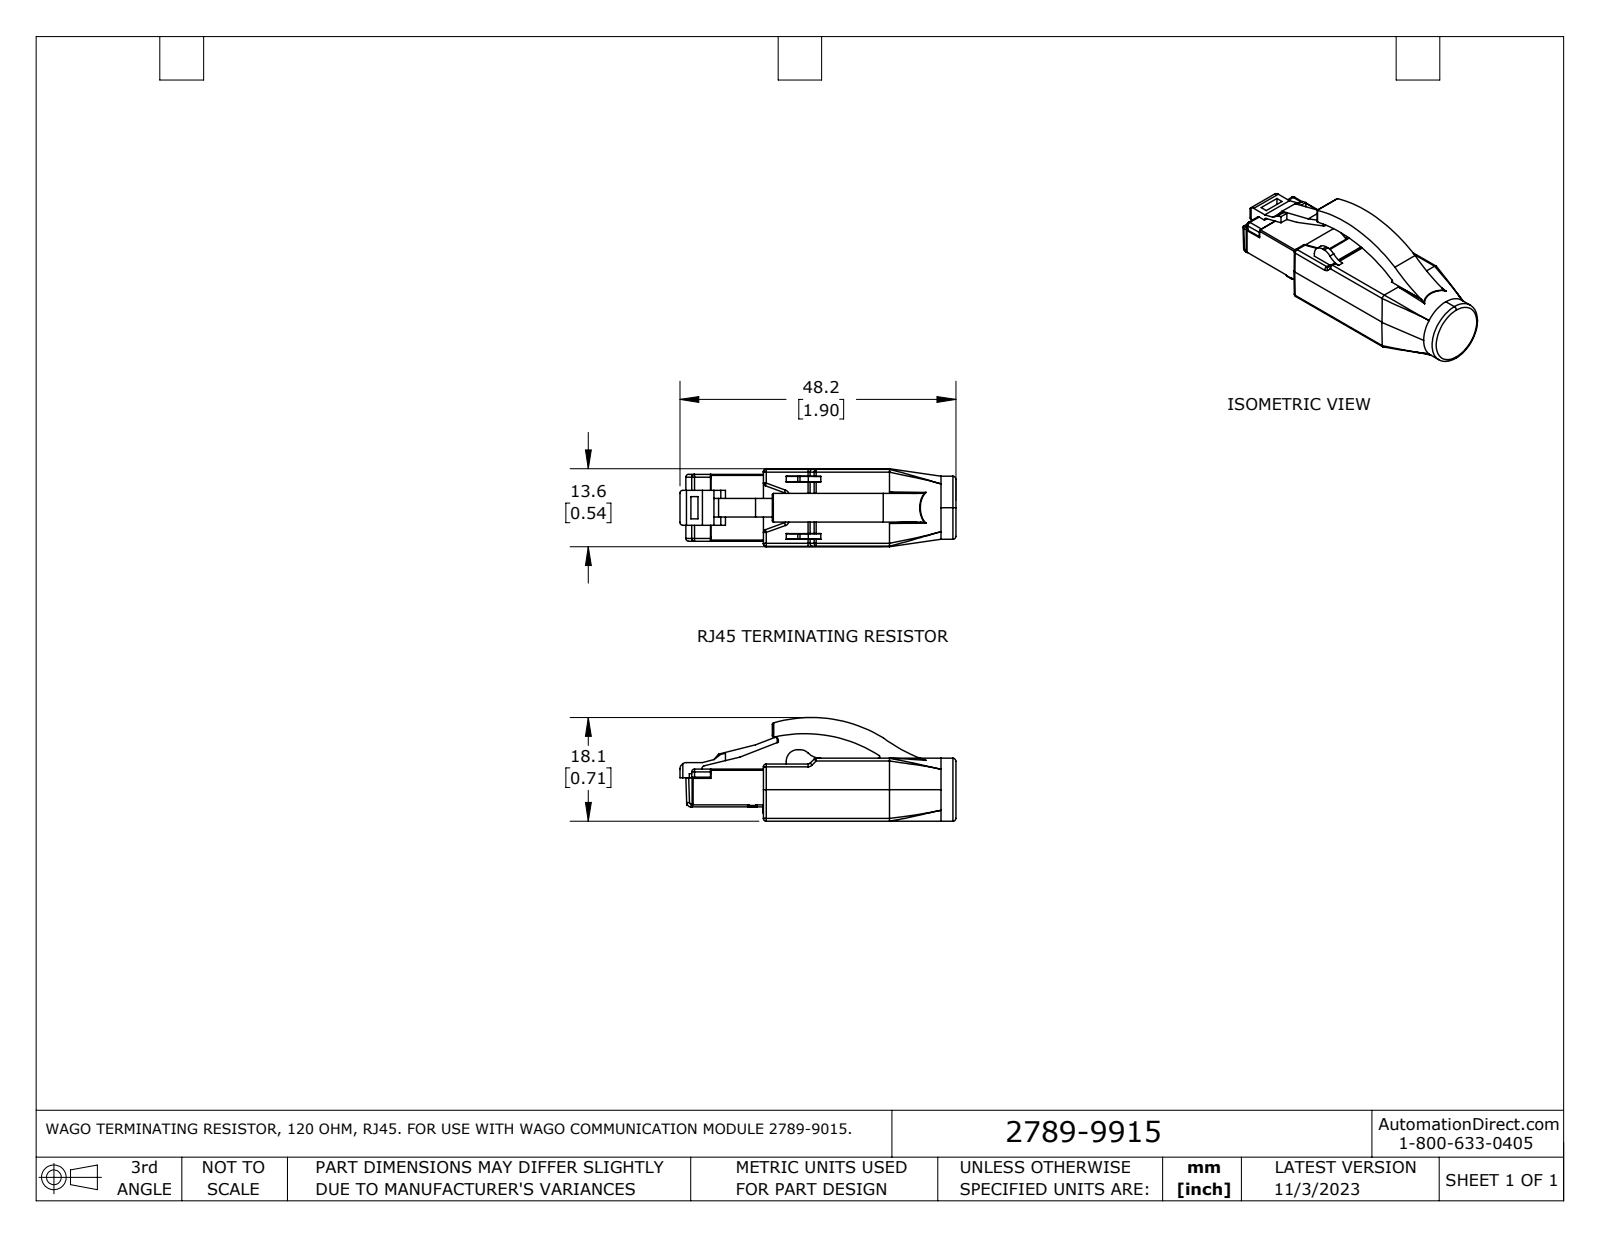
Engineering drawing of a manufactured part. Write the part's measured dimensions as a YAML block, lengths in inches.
part_name: "2789-9915"
step_written_by: "SolidWorks 2023 (AUTOMOTIVE_DESIGN)"
units: inches
bodies: {solids: 1, faces: 314, planar: 193, cylindrical: 90, other: 31}
overall_size: [1.897, 0.713, 0.536]
volume: 0.358
surface_area: 5.434
round_bosses_or_shafts:
  - {diameter: 0.433, count: 1}
partial_cylinders:
  - {radius: 0.02, count: 37}
  - {radius: 0.008, count: 15}
  - {radius: 0.01, count: 5}
  - {radius: 0.006, count: 2}
  - {radius: 0.079, count: 2}
  - {radius: 0.197, count: 2}
  - {radius: 0.939, count: 2}
  - {radius: 0.03, count: 1}
face_to_face_distances: [0.535, 0.433, 0.452, 0.075, 0.131, 0.328, 0.124, 0.32, 0.45, 0.122]
